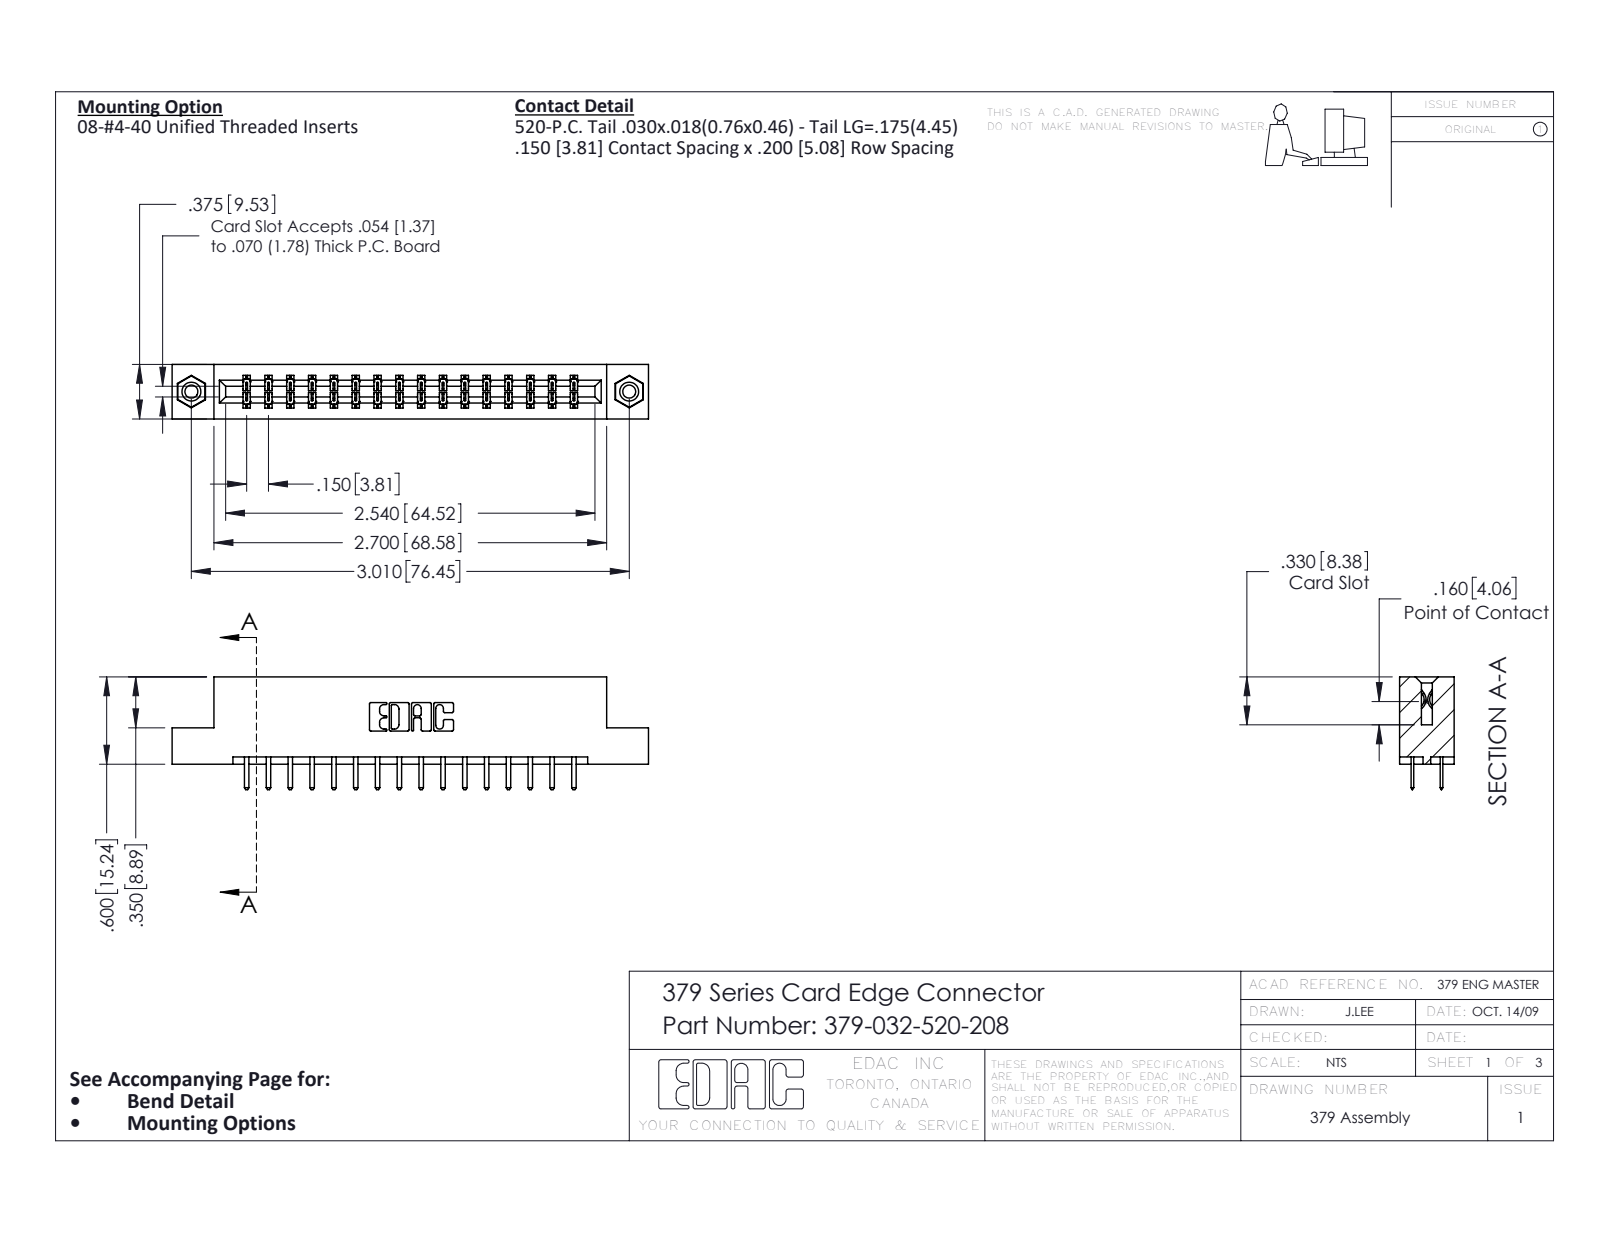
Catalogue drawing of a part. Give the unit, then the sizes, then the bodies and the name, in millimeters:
Units: millimetres
Overall size (bounding box): 83.2 × 19.7 × 9.5
Round holes (diameter × count): ⌀2.3 ×2, ⌀3.2 ×2, ⌀4 ×2
Round bosses / shafts (diameter × count): ⌀3.9 ×2
Partial cylindrical surfaces — rounded edges, fillets, slot ends (radius × count): R0.2 ×63, R0.3 ×36, R0.3 ×22, R0.2 ×6, R0.8 ×6, R0.7 ×3, R0.4 ×2, R0.6 ×2
Main face-to-face distances: 7.6, 9.5, 5.1, 1.9, 2.5, 3.8, 1.3, 15.2, 5.7, 14
Hole centre spacings: 76.5
Volume: 8 520 mm³ · Surface area: 9 310 mm²
Bodies: 35 solids, 1966 faces (1318 planar, 632 cylindrical, 16 other)
Part name (STEP PRODUCT): 345-292-001_345-293-120; 345-250-001_345-250-003-102; 379-032-520-208; 379 Part_Flush - .156 Dia - TI
STEP written by: SolidWorks 2020 (CONFIG_CONTROL_DESIGN)
